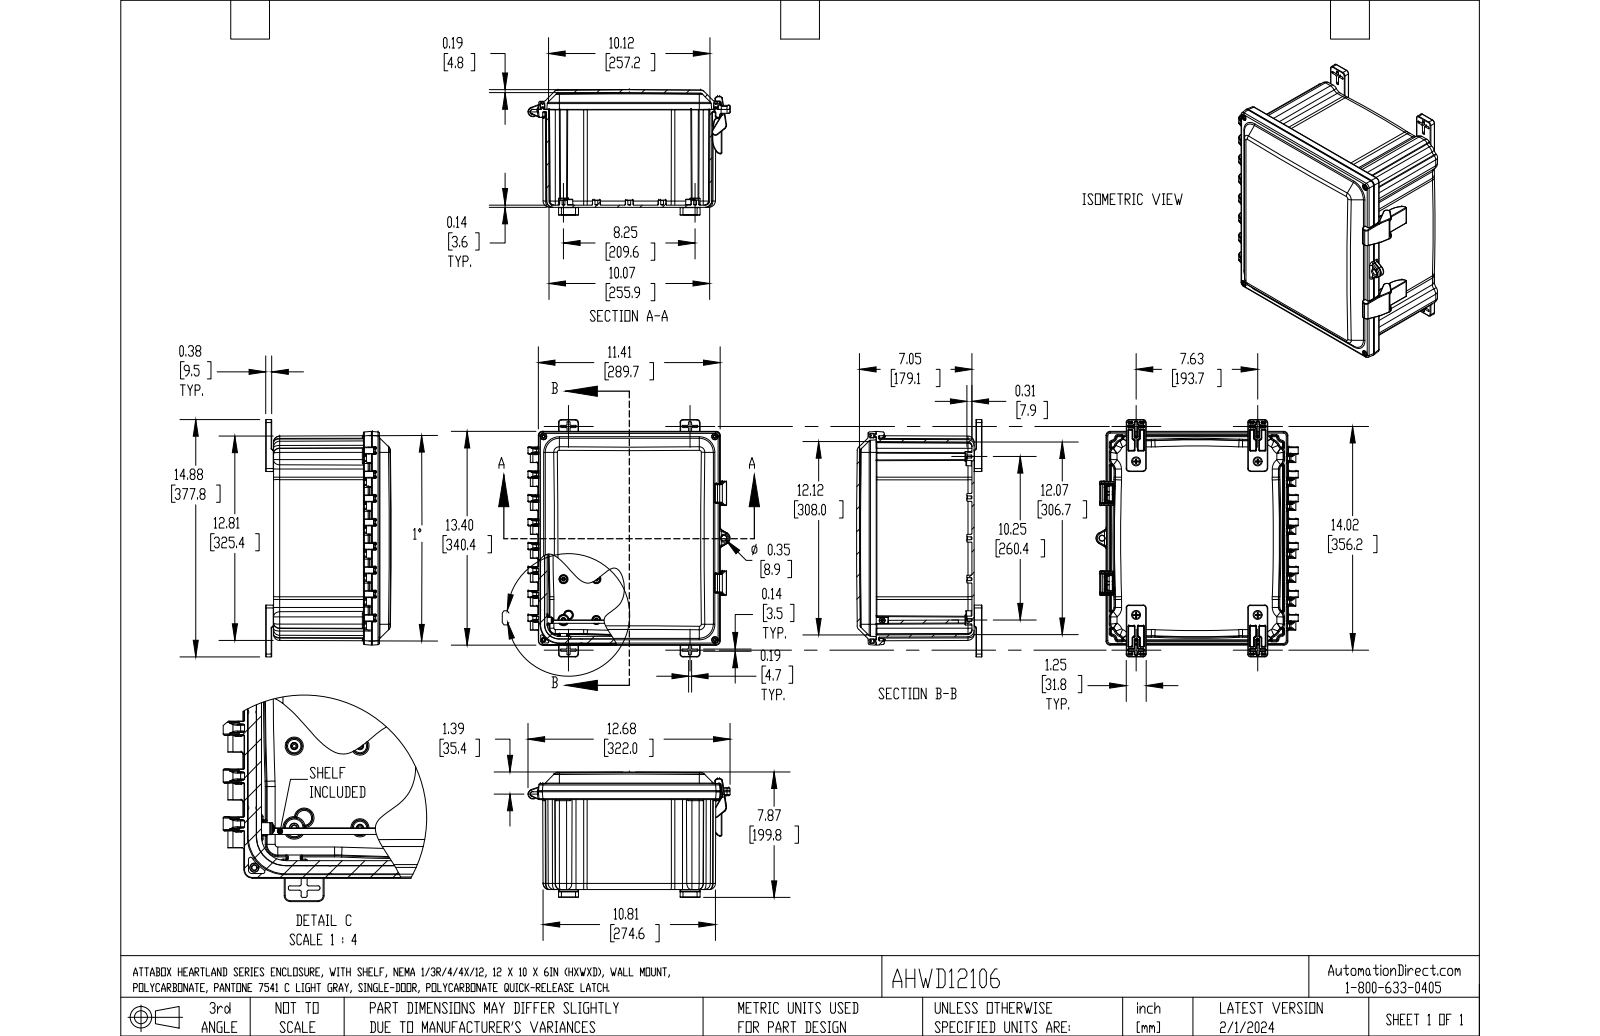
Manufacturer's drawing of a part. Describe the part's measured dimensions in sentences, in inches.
The part is named "AHWD12106". Its 3-D file was written by "SolidWorks 2023 (AUTOMOTIVE_DESIGN)". It is 11 solids with 1855 faces: 650 planar, 633 cylindrical and 572 other. Overall it measures 14.875 by 12.676 by 7.878 inches. Its volume is 126.4 cubic inches and its surface area 1 503 square inches. Round holes: 21 of diameter 0.187, 4 of diameter 0.195, 4 of diameter 0.25, 4 of diameter 0.265, 4 of diameter 0.28, 4 of diameter 0.39, 2 of diameter 0.19, 1 of diameter 0.327, 1 of diameter 0.375, 1 of diameter 0.45. Round bosses or shafts: 21 of diameter 0.487, 4 of diameter 0.625, 4 of diameter 0.25, 2 of diameter 0.373, 2 of diameter 0.2, 2 of diameter 0.19, 1 of diameter 0.313. Partial cylindrical surfaces (rounded edges, fillets, slot ends): 187 of radius 0.035, 52 of radius 0.05, 28 of radius 0.03, 25 of radius 0.065, 22 of radius 0.01, 17 of radius 0.02, 16 of radius 0.18, 16 of radius 0.338. The main face-to-face distances are 0.115, 0.14, 10.115, 12.115, 6.14, 10, 6, 0.29, 0.5, 12. The hole center spacings are 3.289, 2.563, 6.697, 4.856, 5.125, 5.524, 8.034, 6.579.
